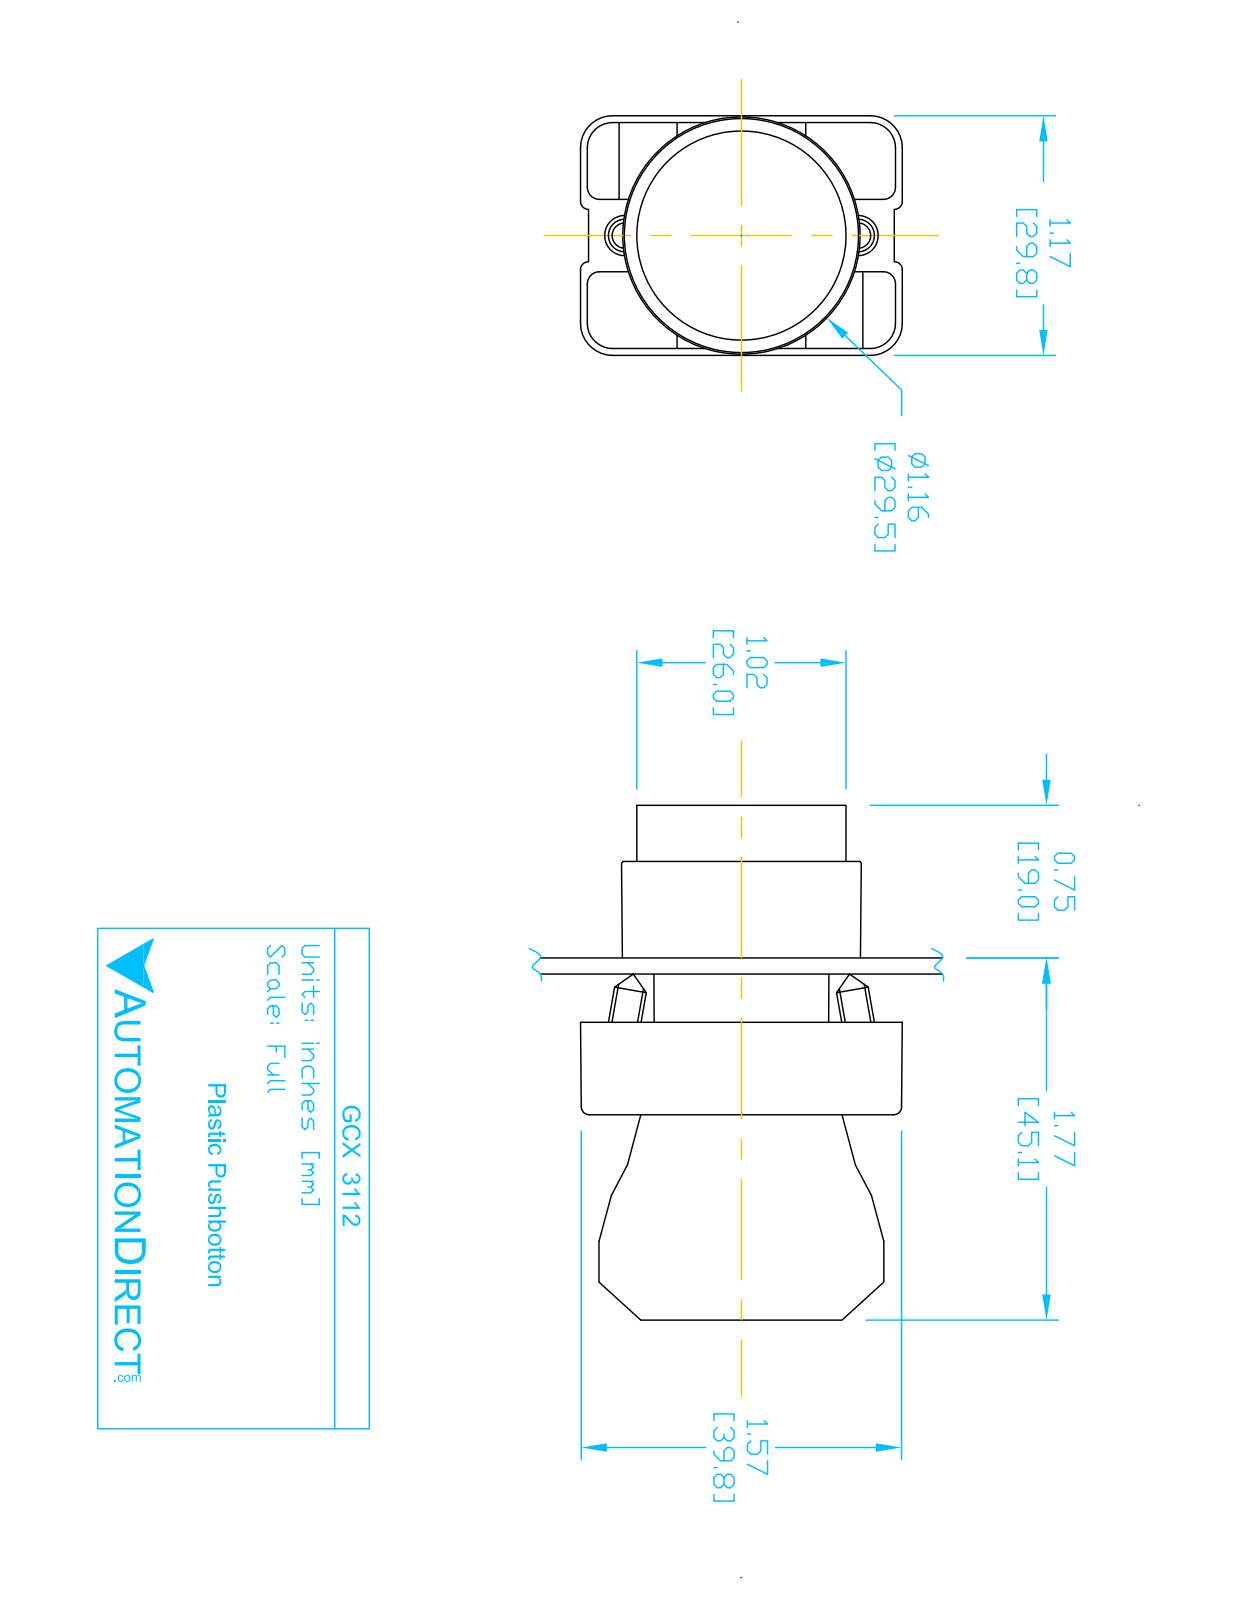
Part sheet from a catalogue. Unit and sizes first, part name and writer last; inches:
Units: inches
Overall size (bounding box): 2.492 × 1.581 × 1.177
Round holes (diameter × count): ⌀0.079 ×2, ⌀0.124 ×2, ⌀0.13 ×2, ⌀0.087 ×1, ⌀0.197 ×1, ⌀0.878 ×1, ⌀0.888 ×1, ⌀1.024 ×1
Round bosses / shafts (diameter × count): ⌀0.157 ×2, ⌀1.175 ×1, ⌀1.004 ×1, ⌀0.945 ×1, ⌀0.856 ×1, ⌀0.78 ×1
Partial cylindrical surfaces — rounded edges, fillets, slot ends (radius × count): R0.059 ×24, R0.041 ×12, R0.124 ×12, R0.157 ×12, R0.039 ×4, R0.128 ×2, R0.02 ×1, R0.063 ×1
Main face-to-face distances: 0.579, 0.033, 1.193, 0.031, 0.472, 0.72, 0.276, 0.689, 0.598, 1.161
Hole centre spacings: 0.236, 0.544, 0.472, 0.49
Volume: 1.584 in³ · Surface area: 26.47 in²
Bodies: 6 solids, 383 faces (222 planar, 132 cylindrical, 29 other)
Part name (STEP PRODUCT): GCX3112 OPERATOR; ECX3029-2; GCX3112; ecx1040
STEP written by: SolidWorks 2016 (AUTOMOTIVE_DESIGN)
